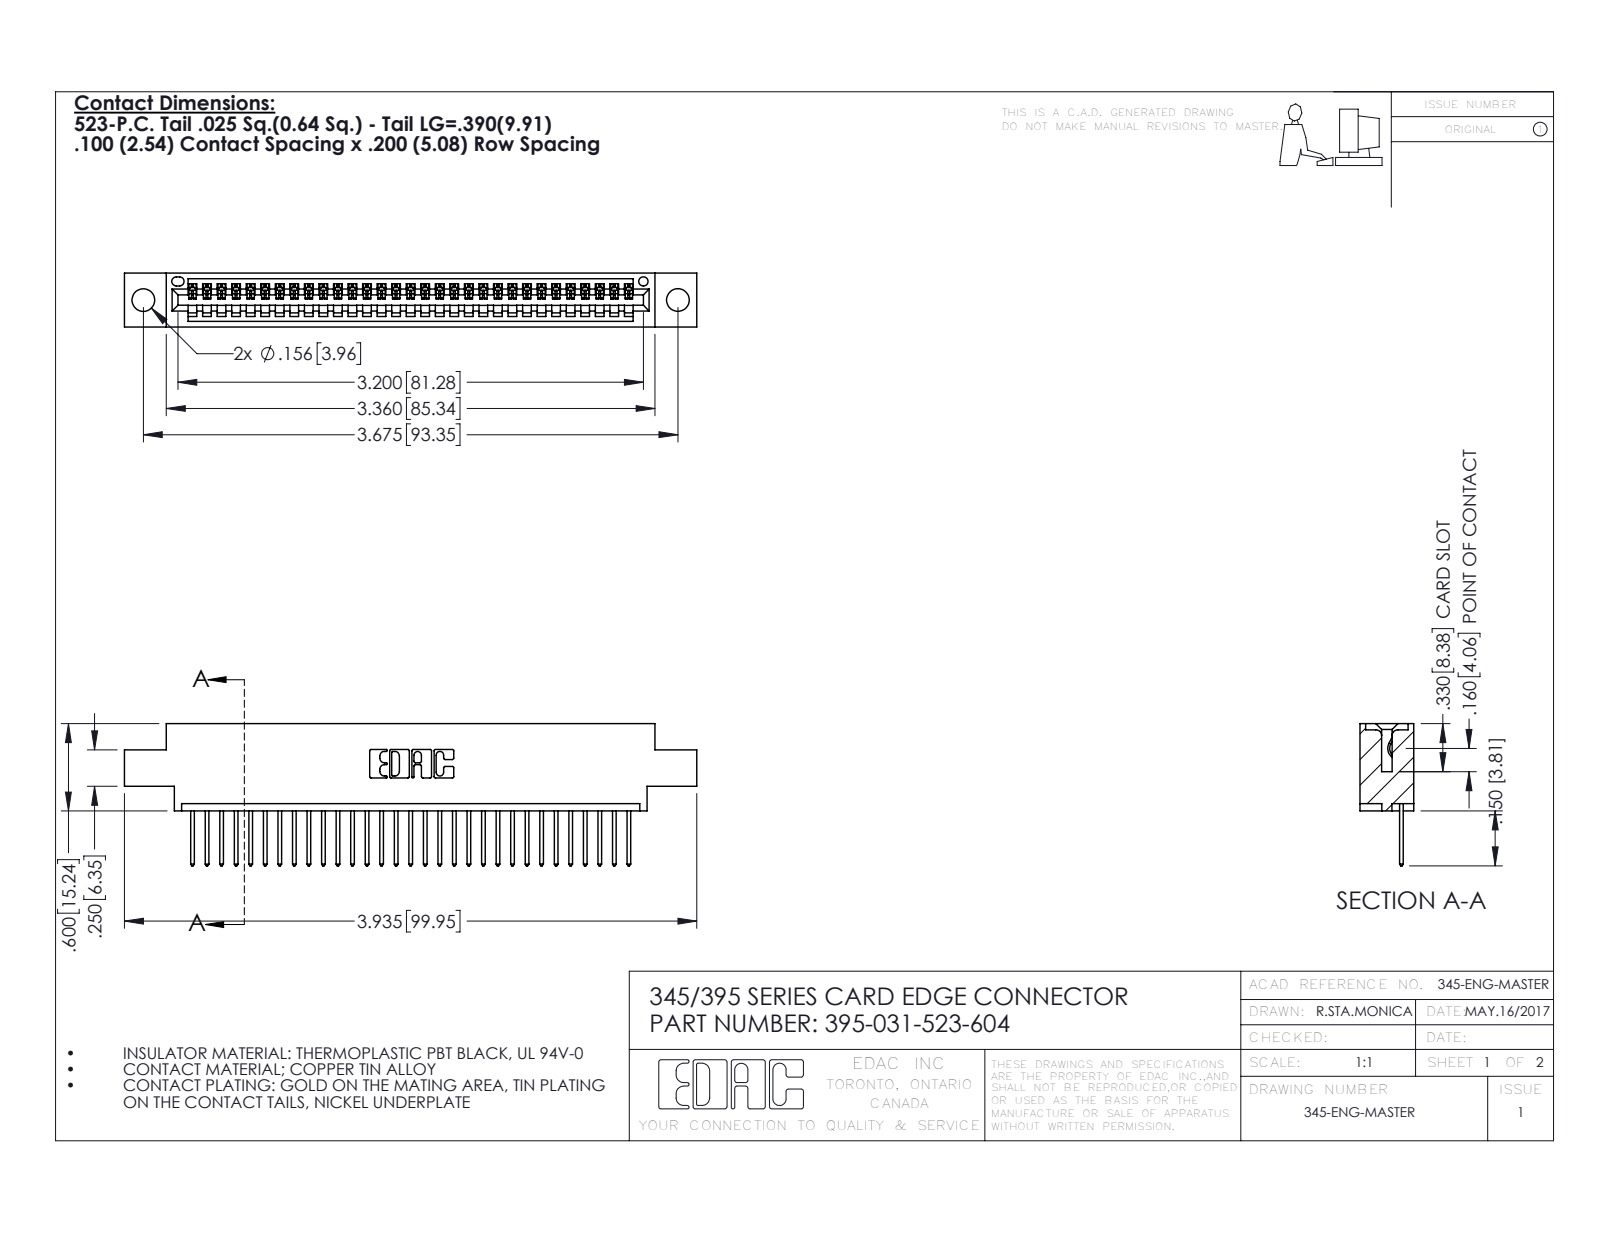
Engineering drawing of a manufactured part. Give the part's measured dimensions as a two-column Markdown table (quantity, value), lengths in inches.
| quantity | value |
| --- | --- |
| part name | 345-292-001_345-293-123; 395-031-523-604; 345 Part_0.170 Offset - 0.156 Dia-TH |
| STEP written by | SolidWorks 2016 (CONFIG_CONTROL_DESIGN) |
| units | inches |
| bodies | 32 solids, 1928 faces (1324 planar, 604 cylindrical, 0 other) |
| overall size | 3.935 × 0.977 × 0.37 |
| volume | 0.561 in³ |
| surface area | 18.65 in² |
| round holes (diameter × count) | 0.156 × 2, 0.064 × 1 |
| partial cylindrical surfaces (radius × count) | 0.006 × 62, 0.01 × 62, 0.01 × 22, 0.007 × 6, 0.031 × 6, 0.026 × 3, 0.031 × 2, 0.04 × 2 |
| main face-to-face distances | 0.298, 0.072, 0.37, 0.2, 0.098, 0.272, 0.025, 0.225, 0.175, 0.149 |
| hole center spacings | 0.27, 3.44, 3.675 |
